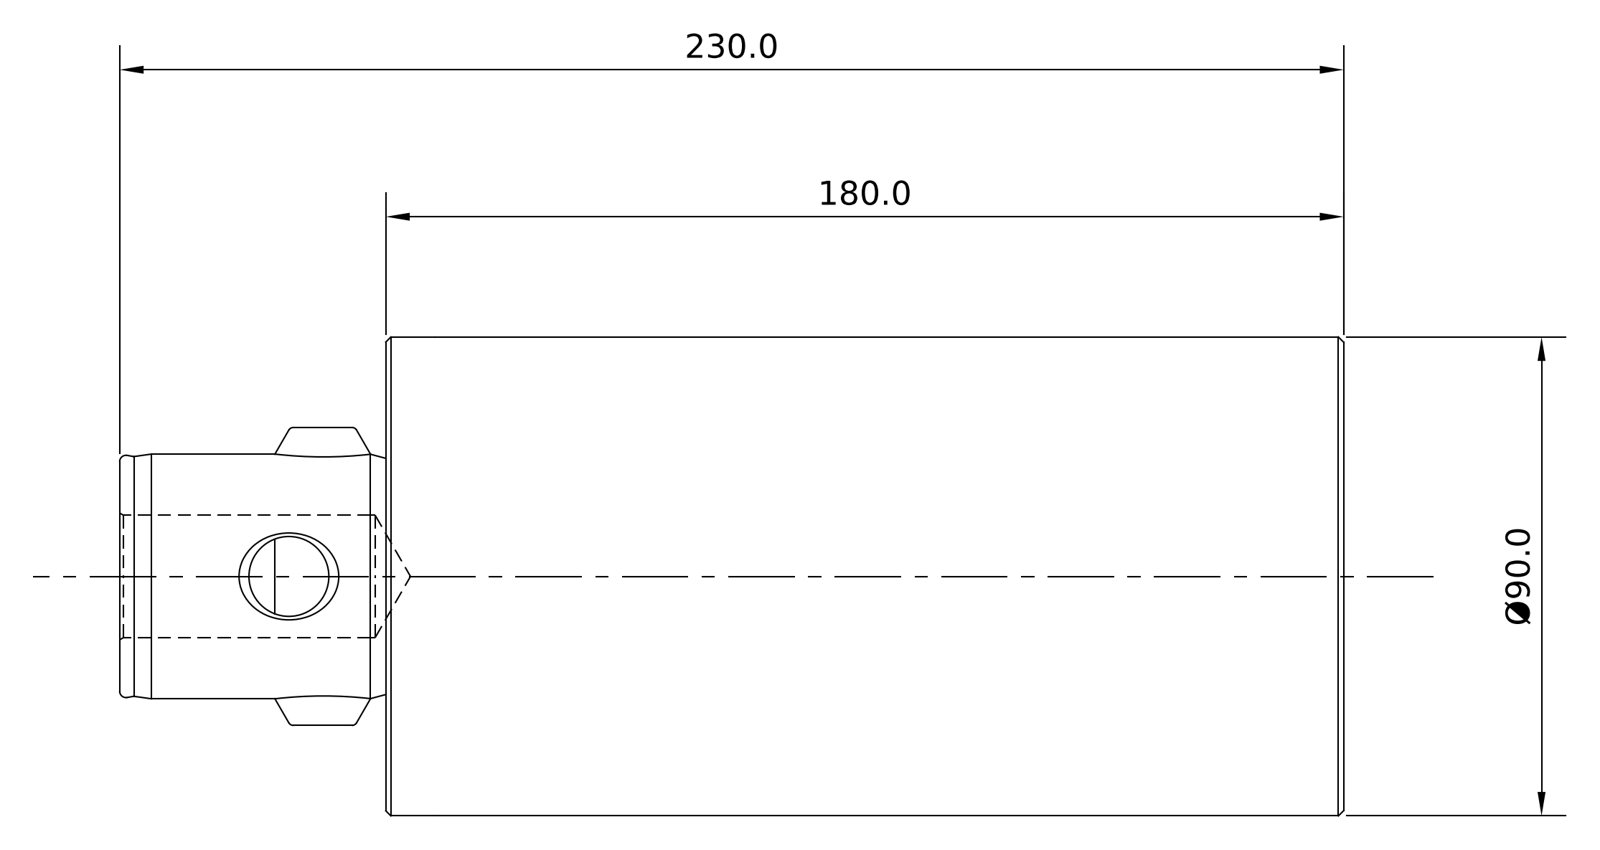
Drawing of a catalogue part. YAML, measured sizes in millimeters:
part_name: "11.335.571; 10.691.50X_10.691.507; 691-50XRing_10.691.507Ring"
step_written_by: "SolidWorks 2009 (CONFIG_CONTROL_DESIGN)"
units: millimeters
bodies: {solids: 3, faces: 81, planar: 19, cylindrical: 29, other: 33}
overall_size: [253.2, 90, 90]
volume: 1358000
surface_area: 84551
round_holes:
  - {diameter: 15, count: 1}
  - {diameter: 18, count: 1}
  - {diameter: 22, count: 1}
  - {diameter: 24.7, count: 1}
round_bosses_or_shafts:
  - {diameter: 90, count: 1}
  - {diameter: 46, count: 1}
  - {diameter: 17.9, count: 1}
  - {diameter: 15.9, count: 1}
  - {diameter: 12, count: 1}
partial_cylinders:
  - {radius: 23, count: 1}
face_to_face_distances: [203.2, 50, 253.2, 5.2, 35.7, 30.5, 20.5, 25.7, 56.2, 3]
